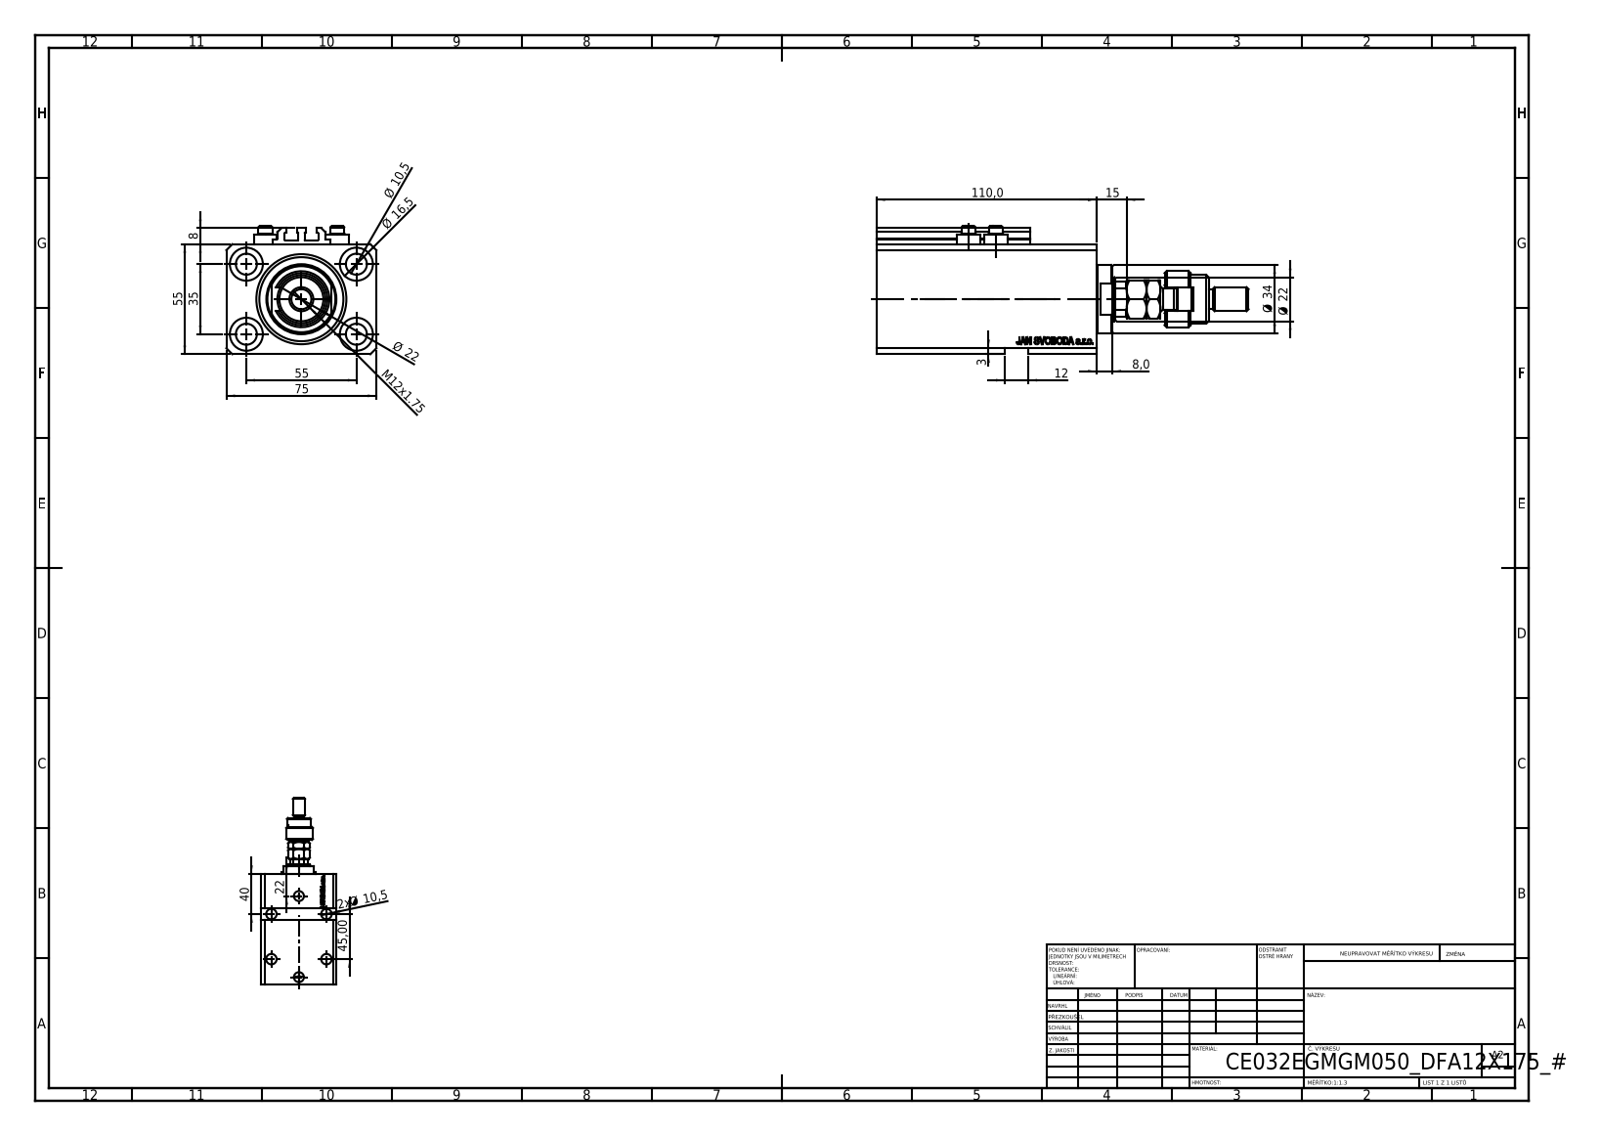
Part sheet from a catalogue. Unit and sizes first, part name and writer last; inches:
Units: inches
Overall size (bounding box): 7.323 × 2.953 × 2.52
Round holes (diameter × count): ⌀0.413 ×9, ⌀0.049 ×4, ⌀0.157 ×4, ⌀0.65 ×4, ⌀0.394 ×2, ⌀0.518 ×2, ⌀0.787 ×2, ⌀0.866 ×1, ⌀1.26 ×1, ⌀1.772 ×1
Round bosses / shafts (diameter × count): ⌀0.457 ×4, ⌀0.276 ×4, ⌀1.339 ×1, ⌀1.102 ×1, ⌀0.945 ×1, ⌀0.709 ×1, ⌀0.472 ×1, ⌀0.433 ×1
Partial cylindrical surfaces — rounded edges, fillets, slot ends (radius × count): R0.008 ×10, R0.384 ×1, R0.413 ×1
Main face-to-face distances: 2.165, 2.953, 0.591, 4.331, 0.118, 3.74, 0.39, 0.315, 0.748, 3.35
Hole centre spacings: 1.283, 1.294, 2.165, 2.706, 0.535, 0.555, 0.907, 1.016
Volume: 24.36 in³ · Surface area: 159.3 in²
Bodies: 10 solids, 1169 faces (542 planar, 159 cylindrical, 468 other)
Part name (STEP PRODUCT): V250CE_VC_E; MFA; V250CE_C_VCP; FEMALE_PART_FOR_DFA (+2 more)
STEP written by: SolidWorks 2019 (CONFIG_CONTROL_DESIGN)
